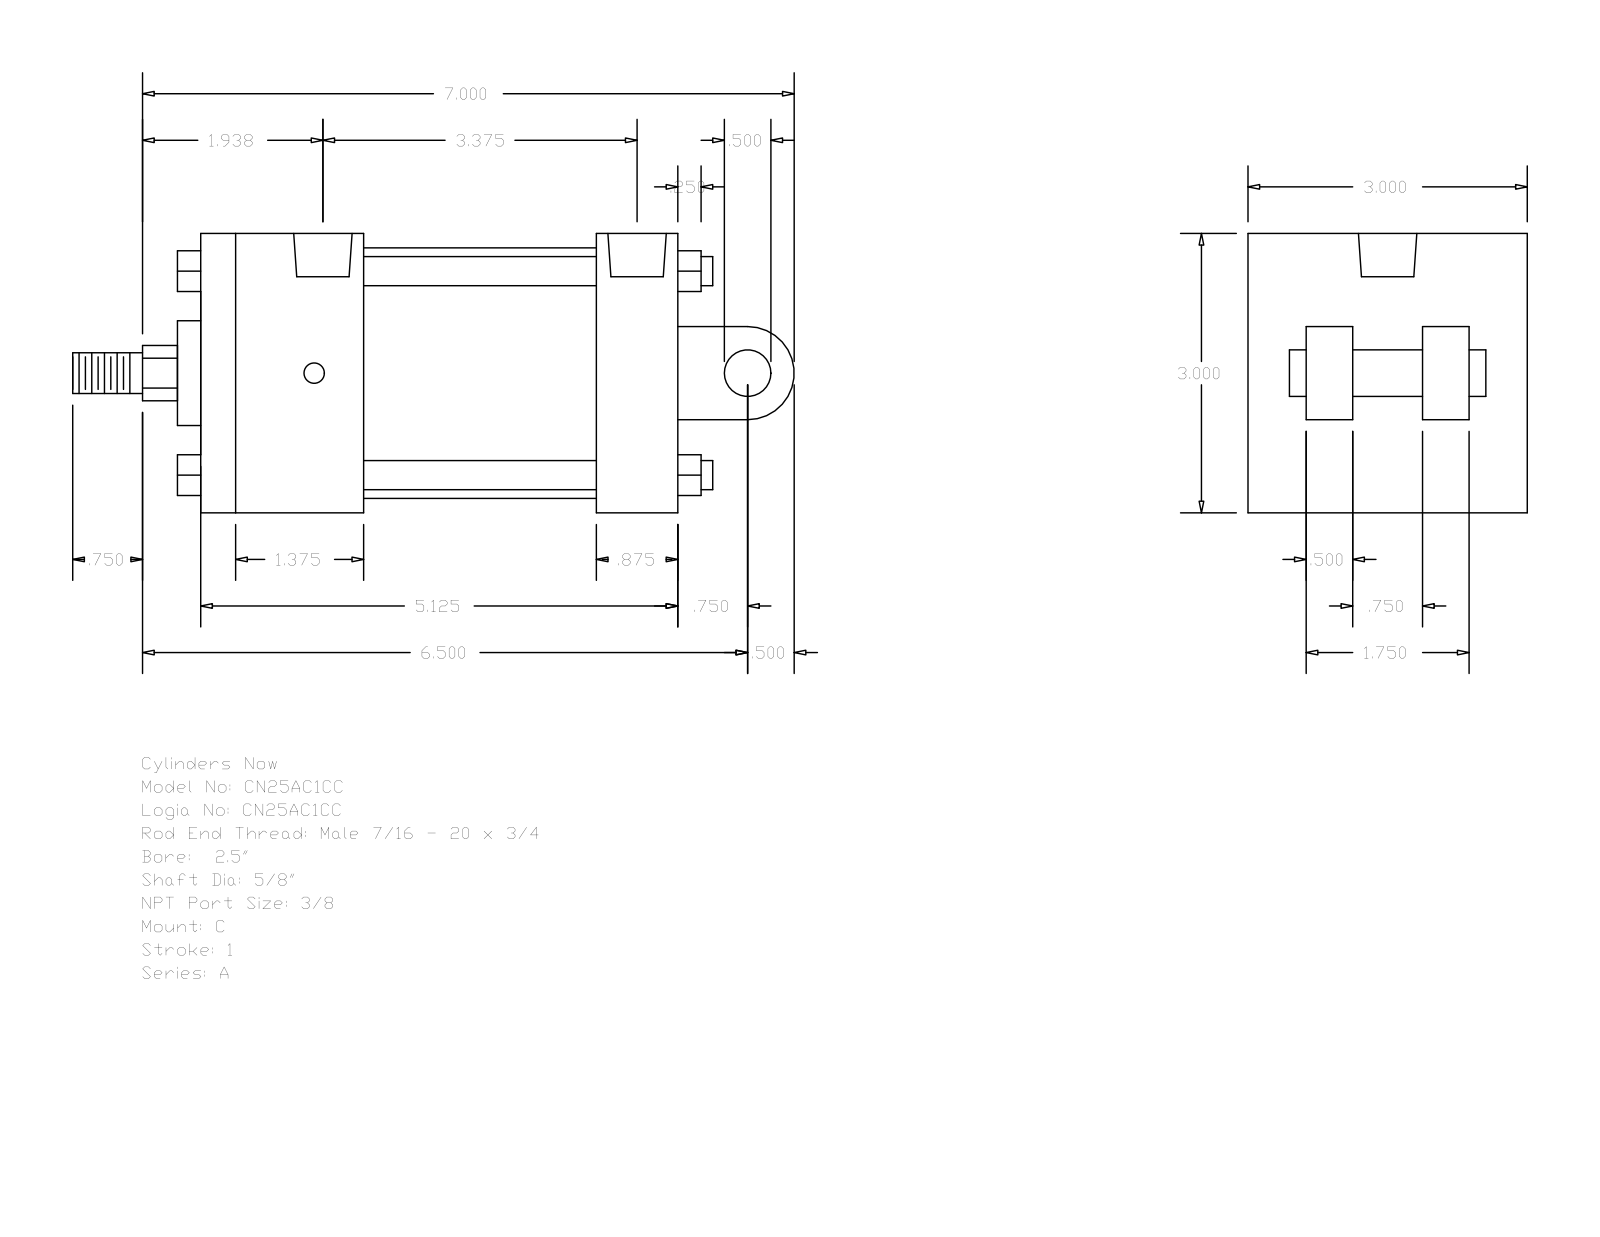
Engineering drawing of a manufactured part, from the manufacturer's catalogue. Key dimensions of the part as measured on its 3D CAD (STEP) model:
Part name (STEP PRODUCT): A_C__0250_0.625
STEP written by: GSSL Pune (CONFIG_CONTROL_DESIGN)
Units: millimetres
Bodies: 0 solids, 135 faces (102 planar, 33 cylindrical, 0 other)
Overall size (bounding box): 196.85 × 76.2 × 76.2
Round holes (diameter × count): ⌀5.56 ×4, ⌀15.93 ×2
Round bosses / shafts (diameter × count): ⌀7.94 ×4, ⌀68.33 ×1, ⌀28.57 ×1, ⌀15.88 ×1, ⌀12.7 ×1, ⌀11.11 ×1
Partial cylindrical surfaces — rounded edges, fillets, slot ends (radius × count): R7.54 ×1, R12.7 ×1
Main face-to-face distances: 76.2, 130.17, 63.5, 44.45, 107.95, 85.72, 22.22, 50.8, 12.7, 25.4
Hole centre spacings: 2.38, 88.11, 90.49, 85.73
